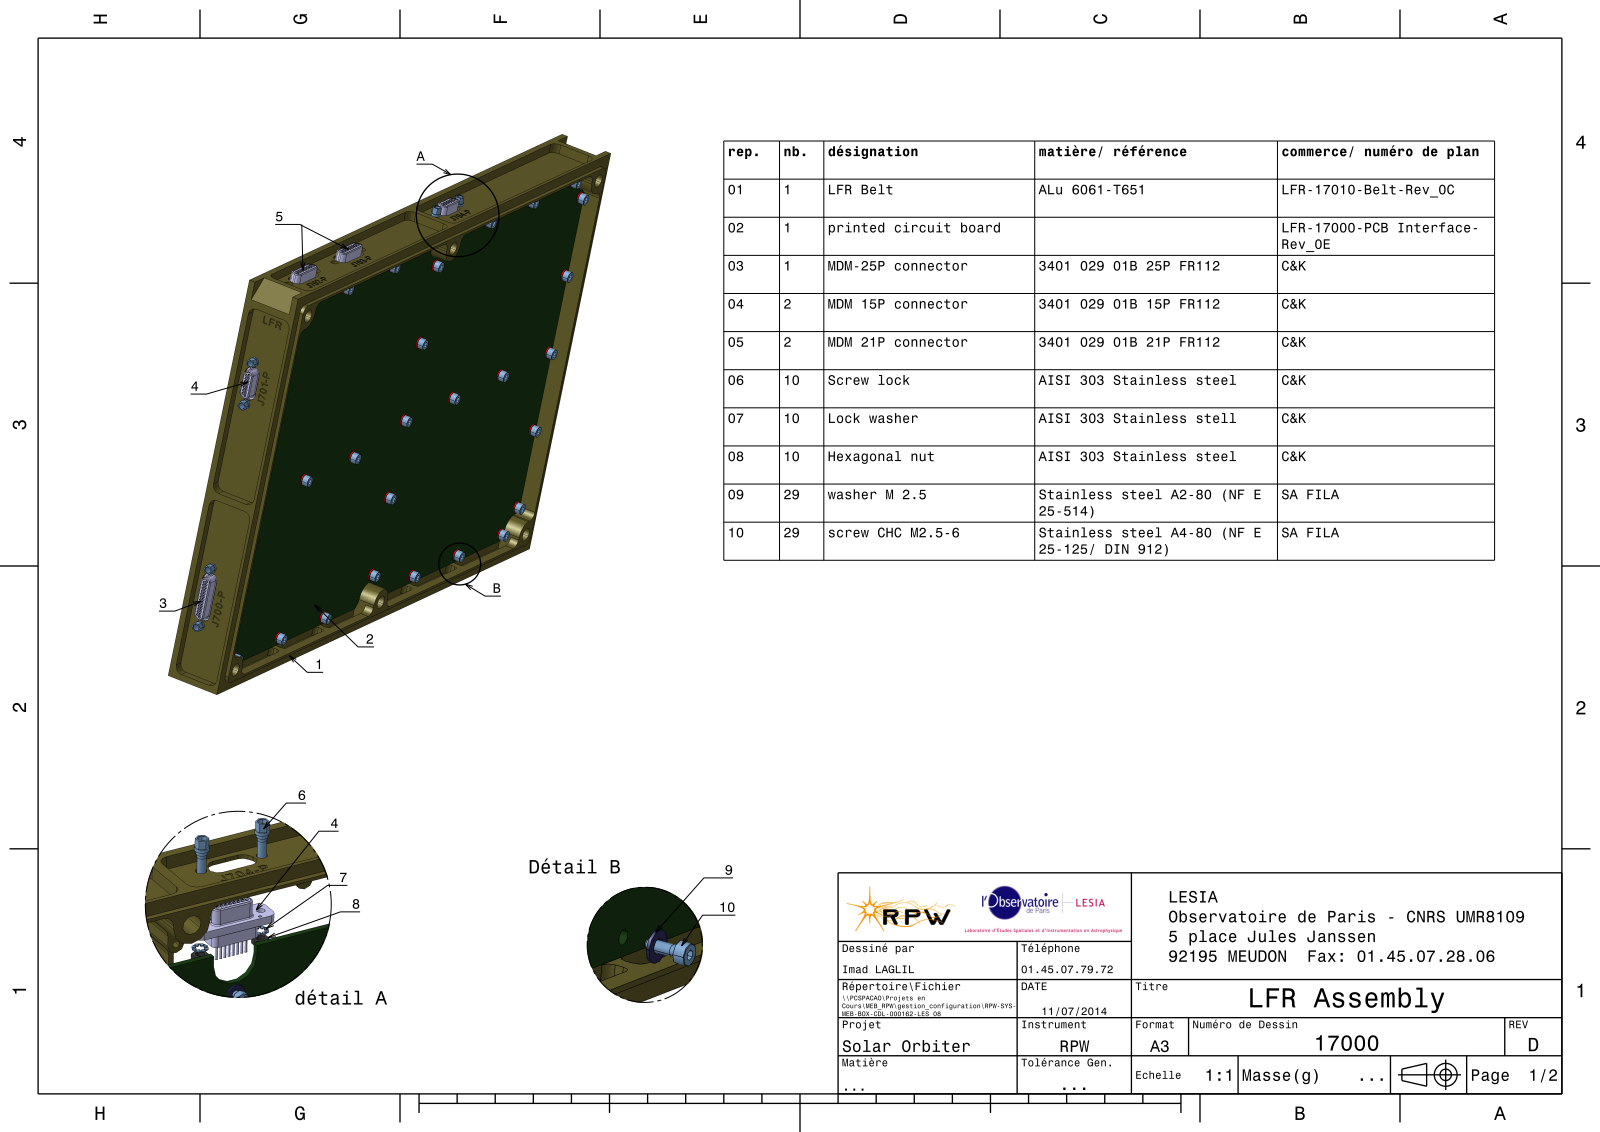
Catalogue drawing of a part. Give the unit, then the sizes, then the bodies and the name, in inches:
Units: inches
Overall size (bounding box): 9.843 × 6.693 × 0.945
Round holes (diameter × count): ⌀0.026 ×97, ⌀0.036 ×97, ⌀0.037 ×97, ⌀0.043 ×97, ⌀0.106 ×39, ⌀0.079 ×29, ⌀0.094 ×10, ⌀0.101 ×10, ⌀0.125 ×10, ⌀0.217 ×6, ⌀0.039 ×5, ⌀0.118 ×1
Round bosses / shafts (diameter × count): ⌀0.031 ×97, ⌀0.02 ×97, ⌀0.197 ×39, ⌀0.098 ×35, ⌀0.177 ×29, ⌀0.096 ×29, ⌀0.017 ×10, ⌀0.157 ×6
Partial cylindrical surfaces — rounded edges, fillets, slot ends (radius × count): R0.118 ×147, R0.028 ×97, R0.012 ×56, R0.045 ×29, R0.028 ×20, R0.033 ×20, R0.038 ×20, R0.04 ×20
Main face-to-face distances: 0.063, 0.059, 0.047, 0.039, 0.531, 6.496, 0.886, 0.098, 6.543, 0.197
Hole centre spacings: 0.05, 0.086, 0.1, 0.15, 0.05, 0.049, 0.2, 0.132
Volume: 7.746 in³ · Surface area: 261.1 in²
Bodies: 101 solids, 6380 faces (1889 planar, 3338 cylindrical, 1153 other)
Part name (STEP PRODUCT): Ensemble LFR Meb 1.3; Frame LFR 1.3; MDM15P_CABLES; LFR Pcb 1.3 (+8 more)
STEP written by: CATIA V5 STEP AP214 (AUTOMOTIVE_DESIGN)
